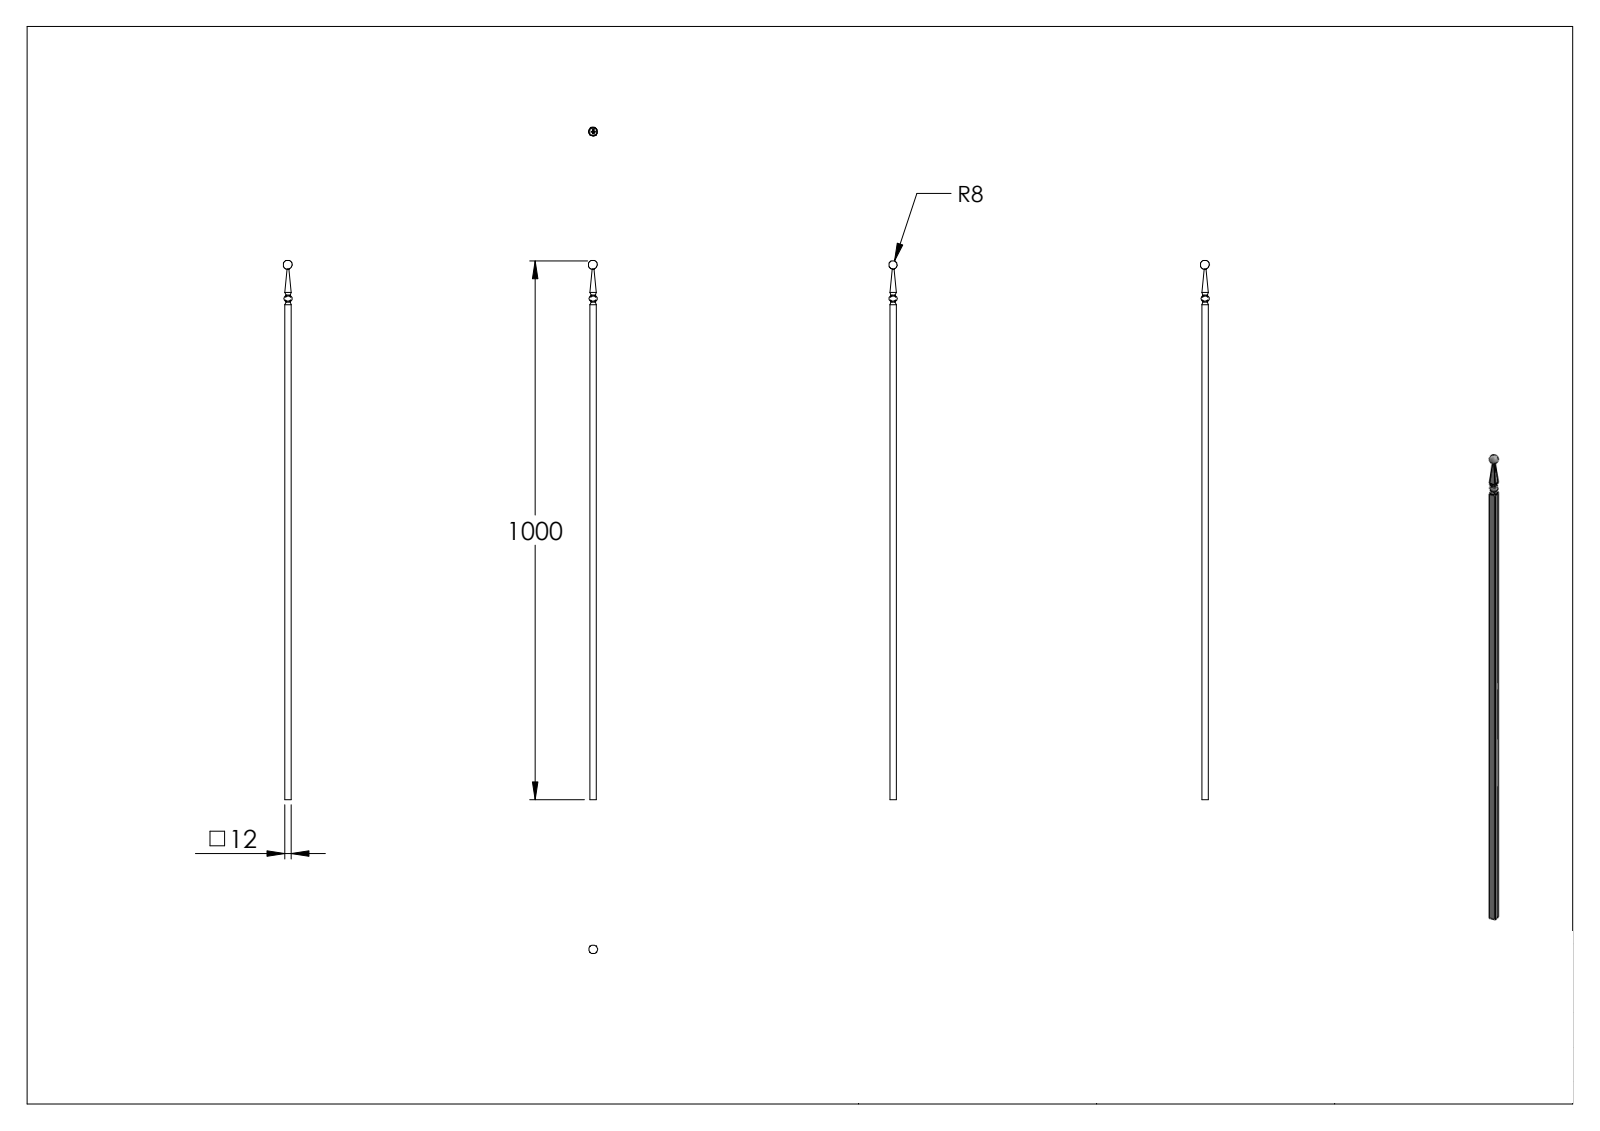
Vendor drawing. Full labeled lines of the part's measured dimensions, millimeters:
Part name (STEP PRODUCT): 18570
STEP written by: SolidWorks 2018 (CONFIG_CONTROL_DESIGN)
Units: millimetres
Bodies: 1 solid, 263 faces (151 planar, 0 cylindrical, 112 other)
Overall size (bounding box): 1000 × 16 × 16
Volume: 139 817 mm³ · Surface area: 47 366 mm²
Main face-to-face distances: 12, 2.78, 2, 10, 8, 4.28, 2.28, 7.72, 5.72, 3.44
